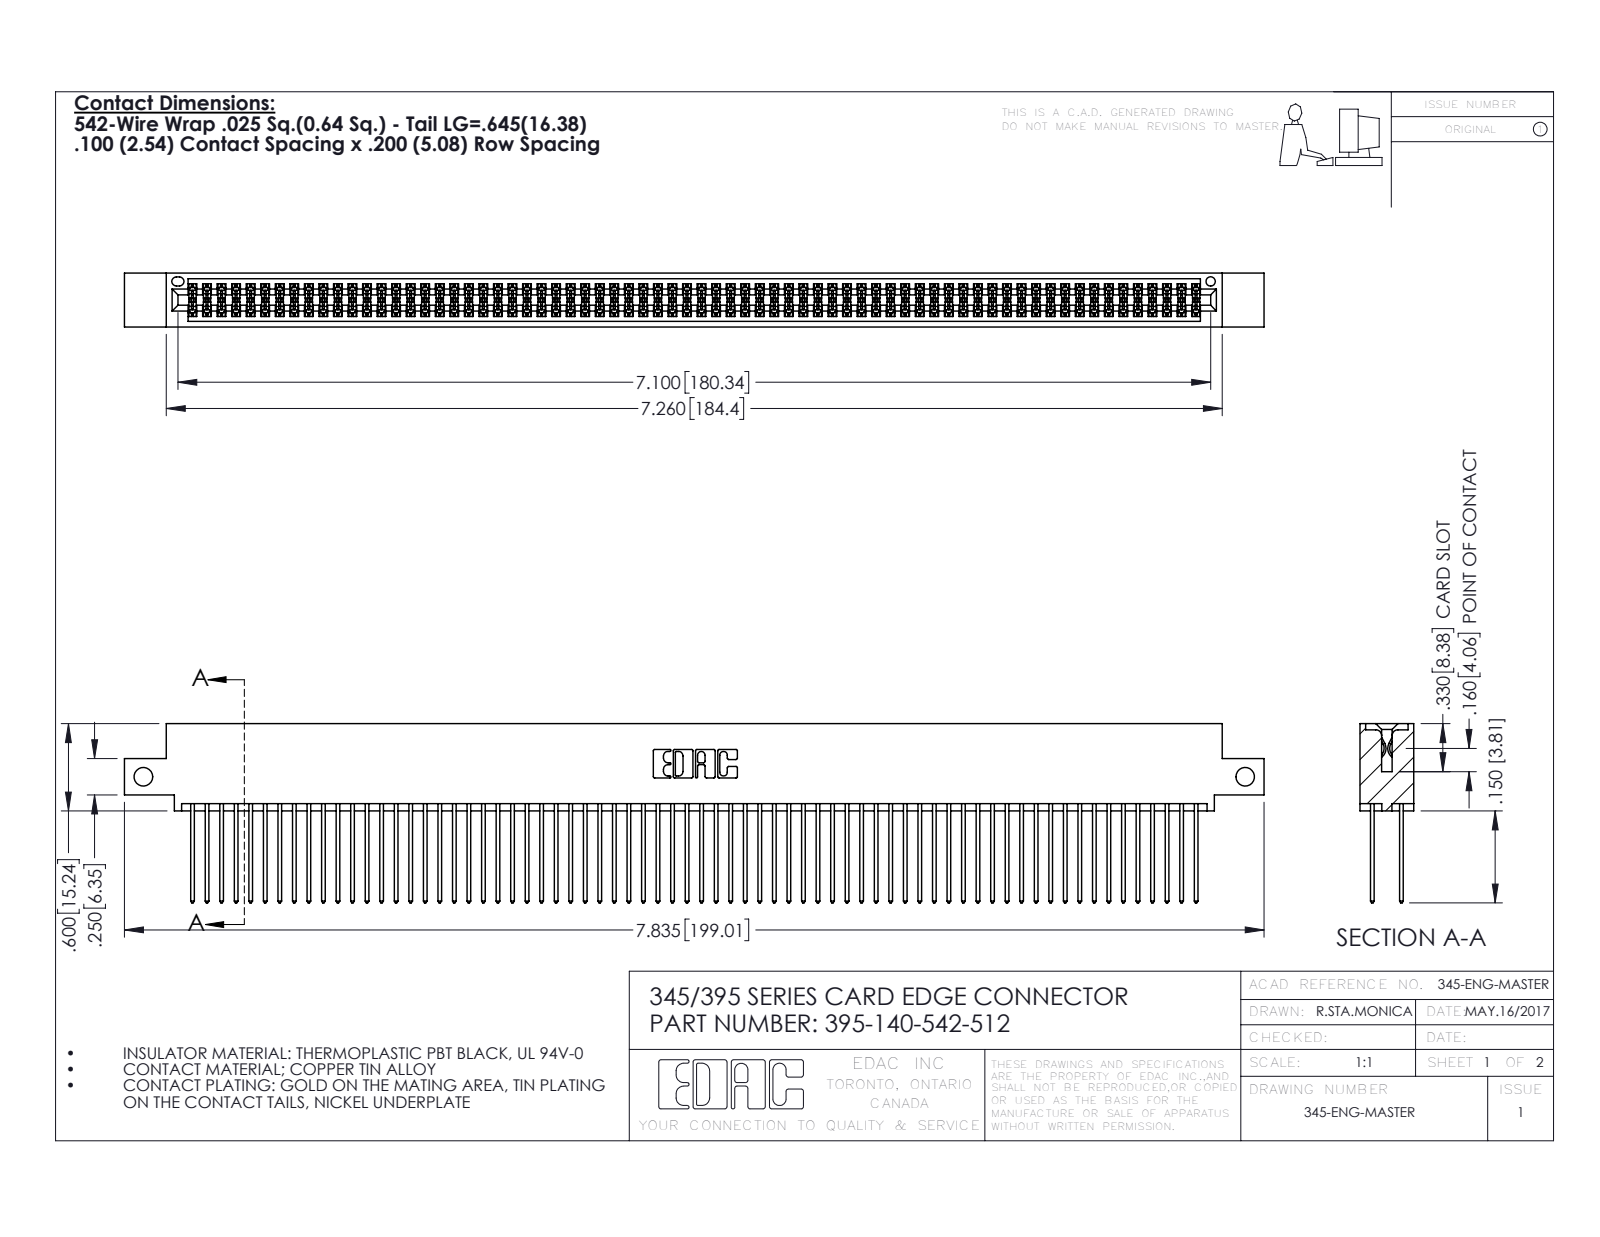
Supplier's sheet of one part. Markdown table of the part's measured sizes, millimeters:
| quantity | value |
| --- | --- |
| part name | 345-292-001_345-293-142; 395-140-542-512; 345 Part_0.110 Offset - Side Mount |
| STEP written by | SolidWorks 2016 (CONFIG_CONTROL_DESIGN) |
| units | millimeters |
| bodies | 141 solids, 7130 faces (4704 planar, 2426 cylindrical, 0 other) |
| overall size | 199 × 31.3 × 9.4 |
| volume | 20 090 mm³ |
| surface area | 33 240 mm² |
| round holes (diameter × count) | 3.3 × 2, 1.6 × 1 |
| partial cylindrical surfaces (radius × count) | 0.2 × 210, 0.3 × 140, 0.3 × 22, 0.2 × 6, 0.8 × 6, 0.7 × 3, 0.4 × 2, 0.5 × 2 |
| main face-to-face distances | 1.8, 7.6, 5.1, 2.5, 6.9, 0.6, 5.7, 9.4, 4.4, 3.8 |
| hole center spacings | 192.4 |
